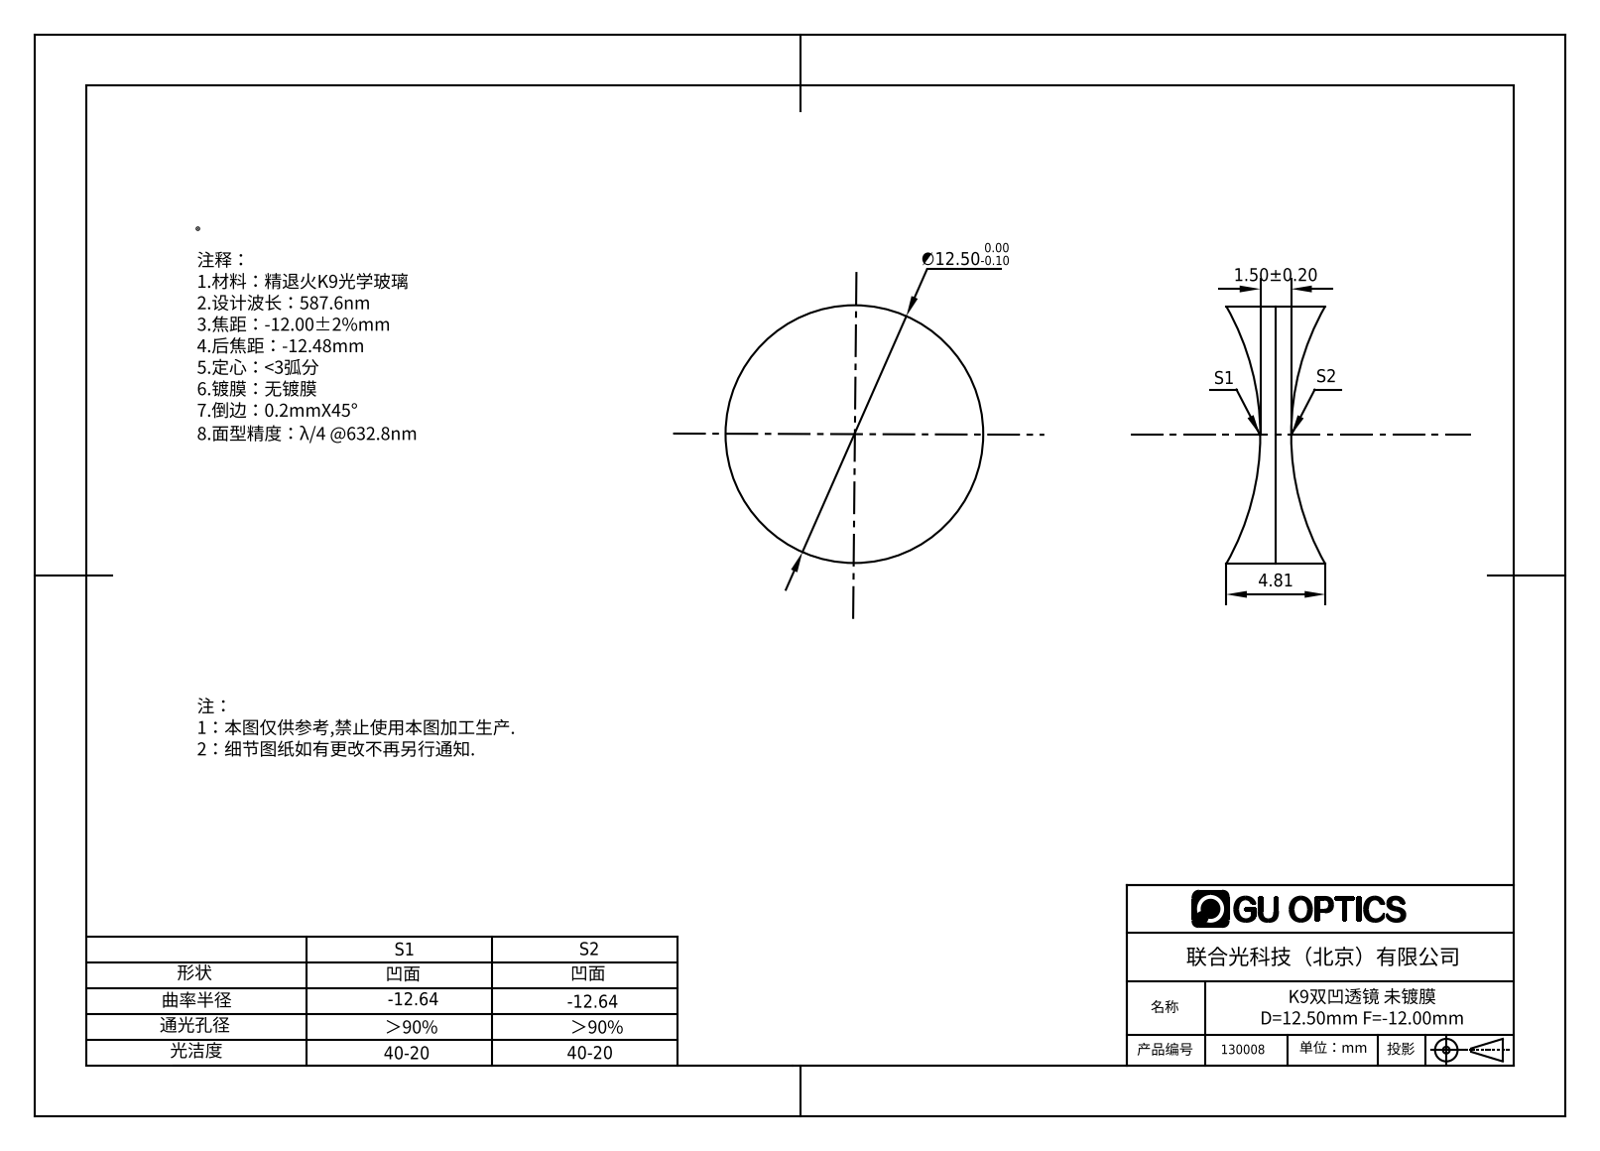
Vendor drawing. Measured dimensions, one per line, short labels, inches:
name: 130008
written by: SolidWorks 2016 (AUTOMOTIVE_DESIGN)
unit: in
bodies: 1 solid, 6 faces (0 planar, 2 cylindrical, 4 other)
size: 0.492 × 0.492 × 0.189
volume: 0.023 in³; area: 0.699 in²
bosses: 1× ⌀0.492
